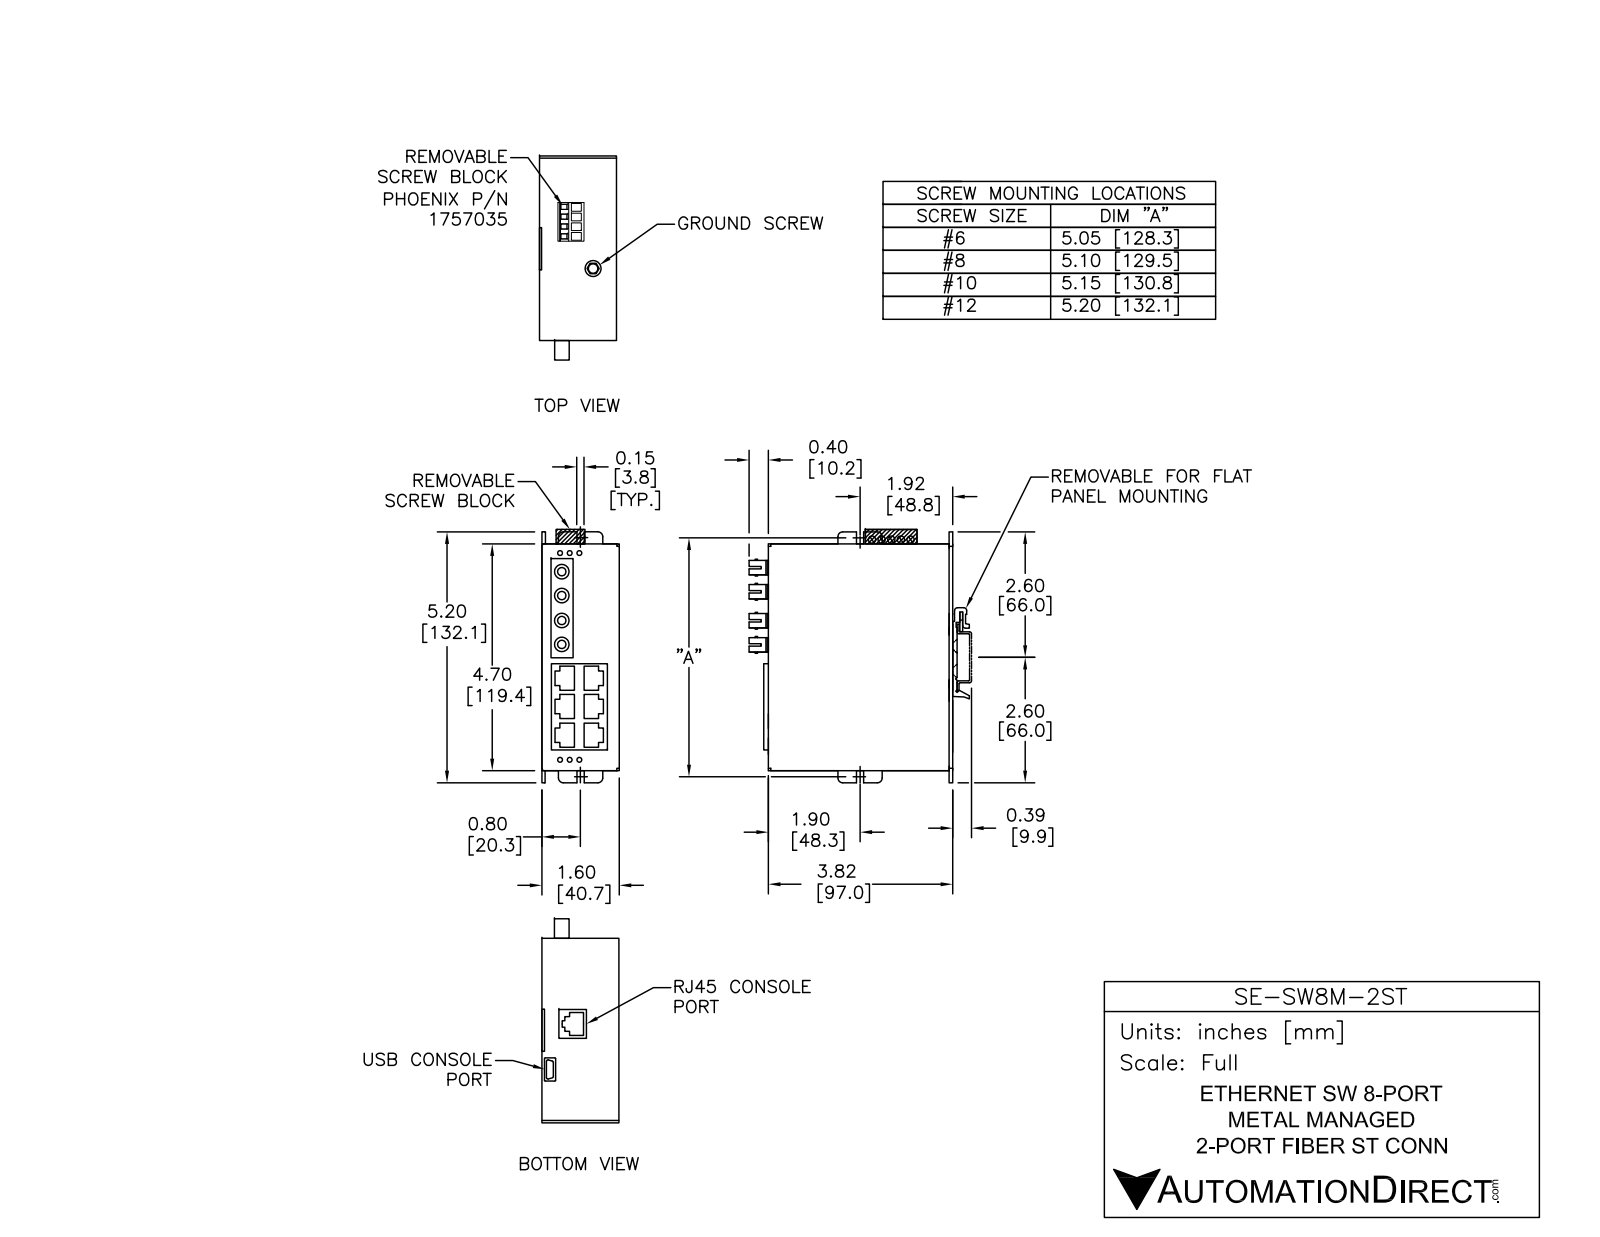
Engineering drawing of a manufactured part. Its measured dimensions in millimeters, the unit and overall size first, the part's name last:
Units: millimetres
Overall size (bounding box): 136.7 × 118.5 × 40.6
Round holes (diameter × count): ⌀2.8 ×6, ⌀4 ×4, ⌀5.5 ×1, ⌀5.6 ×1, ⌀5.6 ×1, ⌀5.6 ×1, ⌀5.7 ×1
Round bosses / shafts (diameter × count): ⌀6.8 ×4, ⌀8.4 ×1
Partial cylindrical surfaces — rounded edges, fillets, slot ends (radius × count): R2.5 ×8, R0.8 ×6, R0.4 ×4, R1.5 ×4, R1.8 ×4, R0.4 ×2, R0.8 ×2, R1.1 ×2
Main face-to-face distances: 1.5, 40.6, 39.1, 1.5, 39.1, 119.4, 1.5, 97, 95.5, 95.5
Hole centre spacings: 111, 4.7, 6.5, 6.9, 12.7, 13.4, 25.8, 111.2
Volume: 472 800 mm³ · Surface area: 79 230 mm²
Bodies: 1 solid, 400 faces (342 planar, 58 cylindrical, 0 other)
Part name (STEP PRODUCT): SE-SW8M-2ST
STEP written by: SolidWorks 2011 (AUTOMOTIVE_DESIGN)
